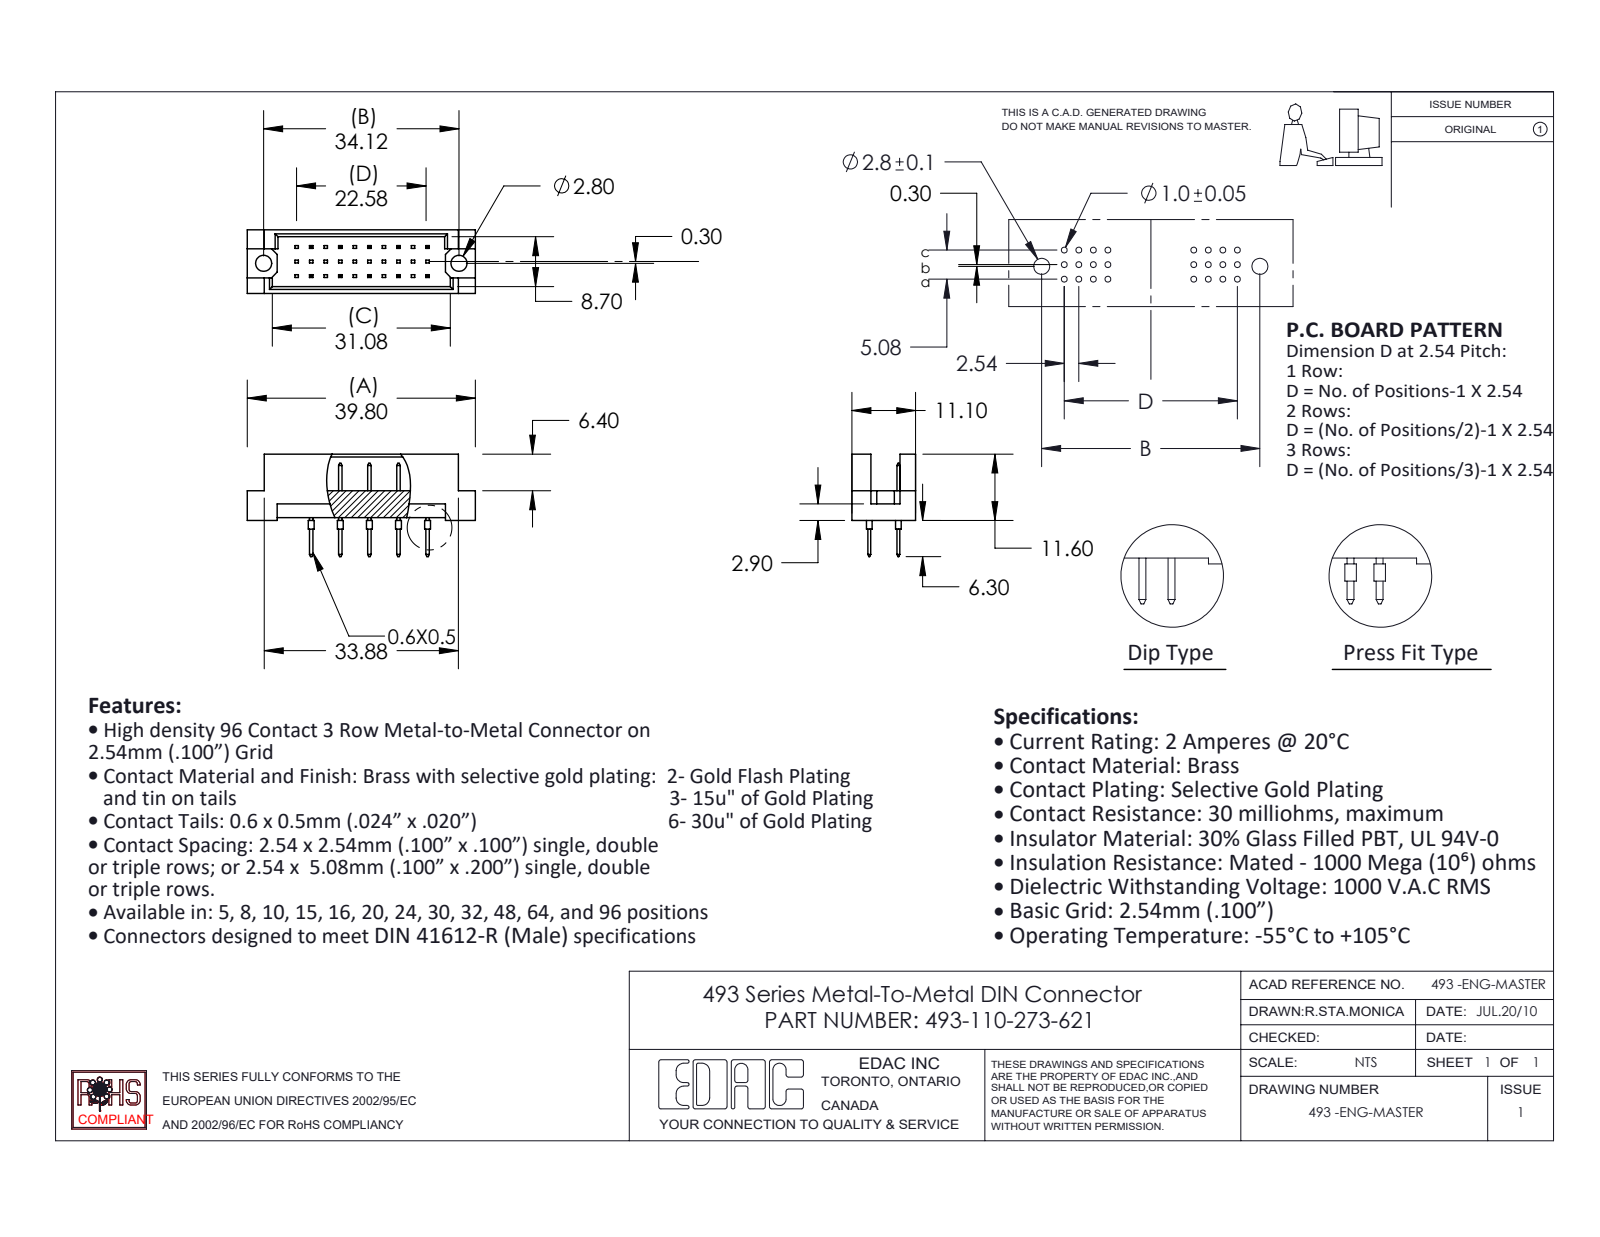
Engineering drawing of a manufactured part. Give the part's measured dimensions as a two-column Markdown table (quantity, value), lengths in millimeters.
| quantity | value |
| --- | --- |
| part name | 493 Part_30; 493-110-273-622; 493-290_73 |
| STEP written by | SolidWorks 2020 (CONFIG_CONTROL_DESIGN) |
| units | millimeters |
| bodies | 11 solids, 392 faces (368 planar, 24 cylindrical, 0 other) |
| overall size | 39.8 × 17.9 × 11.1 |
| volume | 2 428 mm³ |
| surface area | 3 116 mm² |
| round holes (diameter × count) | 2.8 × 2 |
| round bosses / shafts (diameter × count) | 1 × 10 |
| main face-to-face distances | 1.2, 9.9, 11.1, 5.08, 8.7, 0.5, 4.7, 2.76, 3.26, 7.84 |
| hole center spacings | 34.12 |
